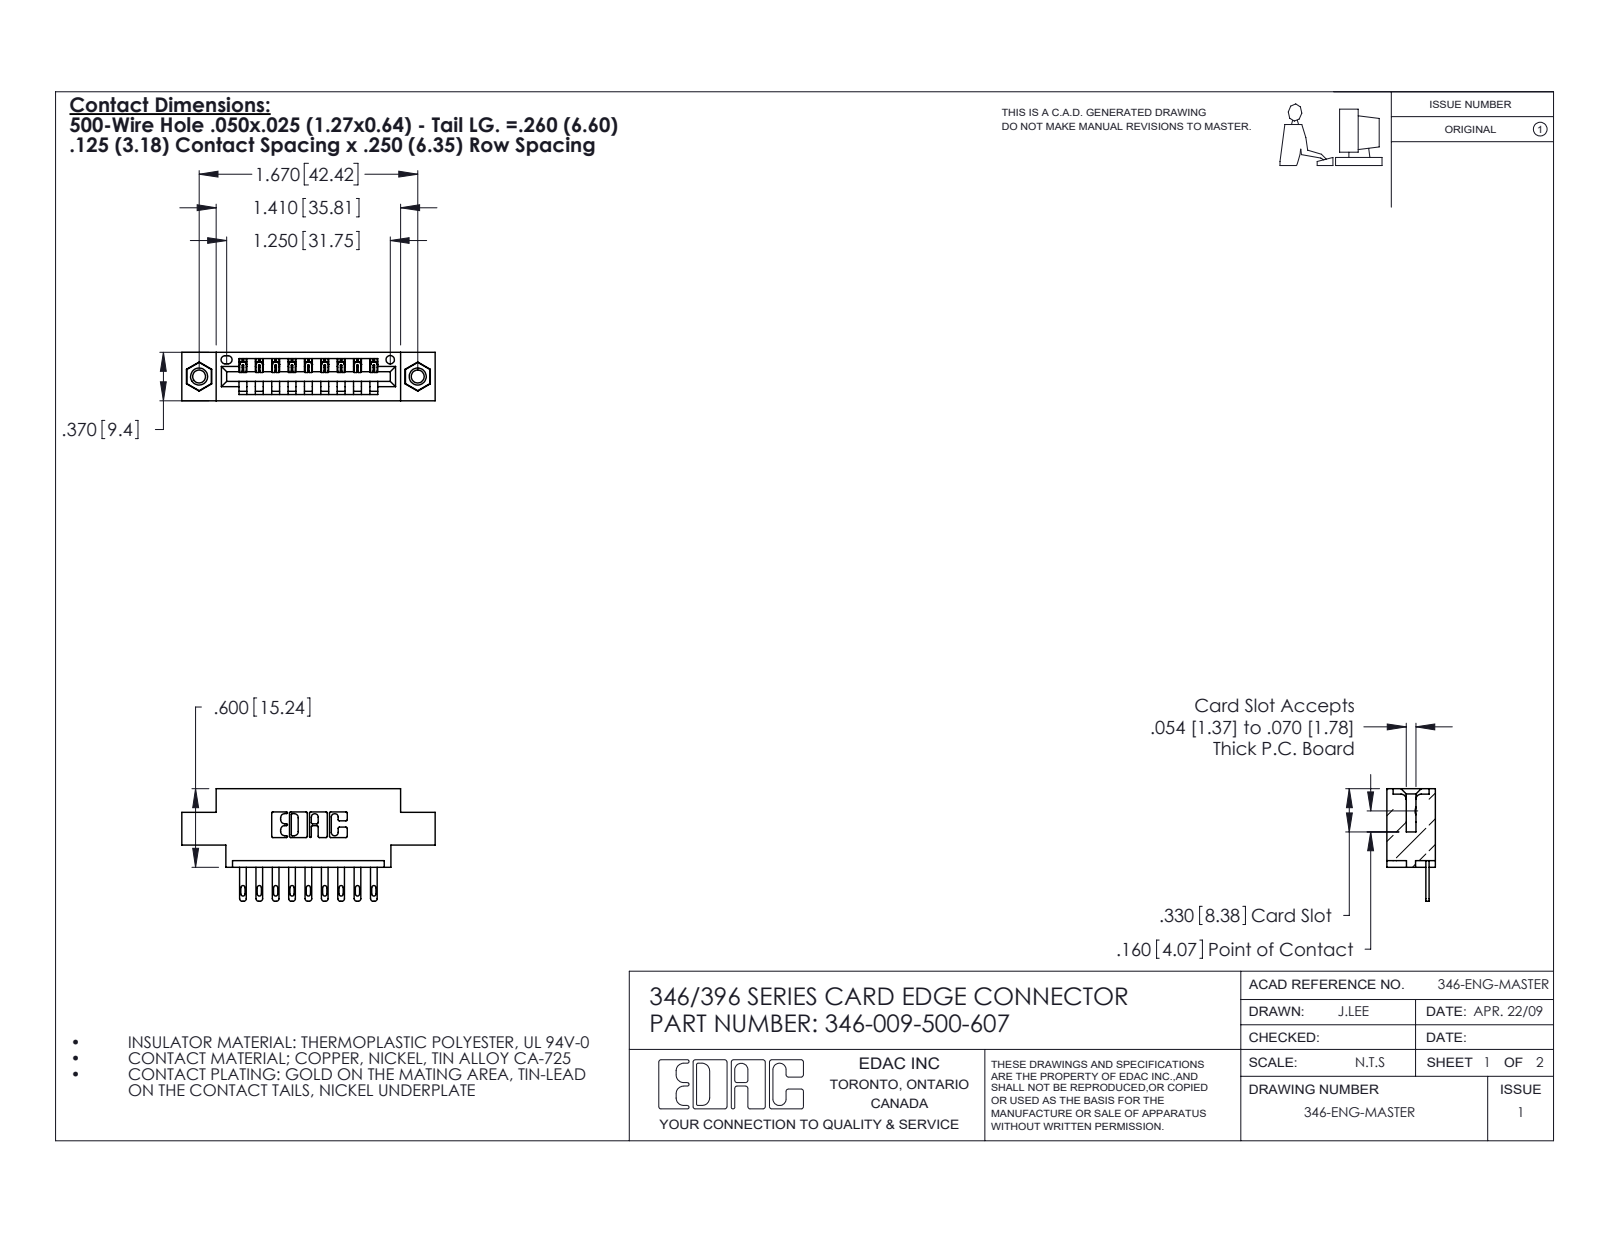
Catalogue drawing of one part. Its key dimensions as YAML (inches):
part_name: "345-292-001_345-293-100; 345-250-001_345-250-005-103; 346-009-500-607; 346 Part_0.170 Offset - 0.156 Dia-TI"
step_written_by: "SolidWorks 2020 (CONFIG_CONTROL_DESIGN)"
units: inches
bodies: {solids: 12, faces: 672, planar: 418, cylindrical: 238, other: 16}
overall_size: [1.935, 0.86, 0.37]
volume: 0.263
surface_area: 8.142
round_holes:
  - {diameter: 0.098, count: 2}
  - {diameter: 0.125, count: 2}
  - {diameter: 0.156, count: 2}
  - {diameter: 0.064, count: 1}
round_bosses_or_shafts:
  - {diameter: 0.155, count: 2}
partial_cylinders:
  - {radius: 0.01, count: 22}
  - {radius: 0.006, count: 18}
  - {radius: 0.016, count: 18}
  - {radius: 0.02, count: 18}
  - {radius: 0.007, count: 6}
  - {radius: 0.031, count: 6}
  - {radius: 0.026, count: 3}
  - {radius: 0.031, count: 2}
face_to_face_distances: [0.25, 0.37, 0.048, 0.322, 0.072, 0.298, 0.025, 0.222, 0.148, 0.1]
hole_center_spacings: [0.246, 1.465, 1.67]
